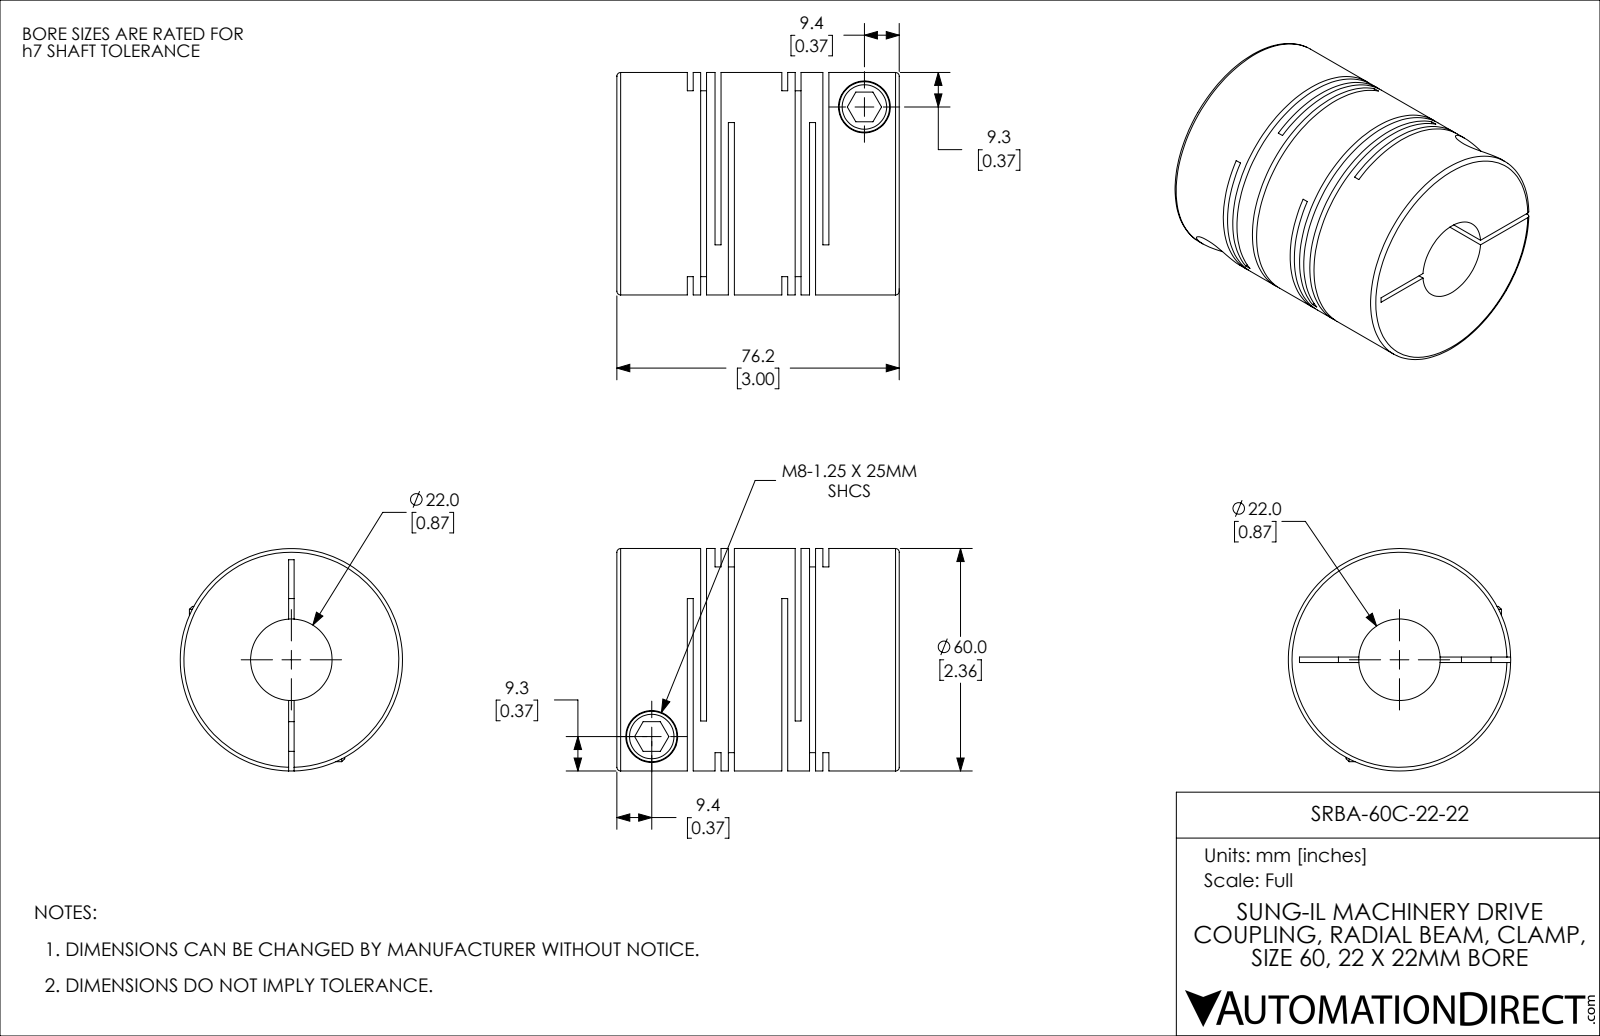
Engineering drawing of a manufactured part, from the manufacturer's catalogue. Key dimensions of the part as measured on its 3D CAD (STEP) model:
Part name (STEP PRODUCT): SRBA-60C-22-22
STEP written by: SolidWorks 2021 (CONFIG_CONTROL_DESIGN)
Units: inches
Bodies: 1 solid, 115 faces (60 planar, 42 cylindrical, 13 other)
Overall size (bounding box): 3 × 2.362 × 2.362
Volume: 9.533 in³ · Surface area: 90.2 in²
Round holes (diameter × count): ⌀0.315 ×2, ⌀0.551 ×2, ⌀0.866 ×1
Round bosses / shafts (diameter × count): ⌀0.535 ×2, ⌀2.362 ×1
Main face-to-face distances: 0.063, 0.142, 0.295, 1.004, 1.299, 0.709, 0.079, 0.232, 0.941, 0.154
